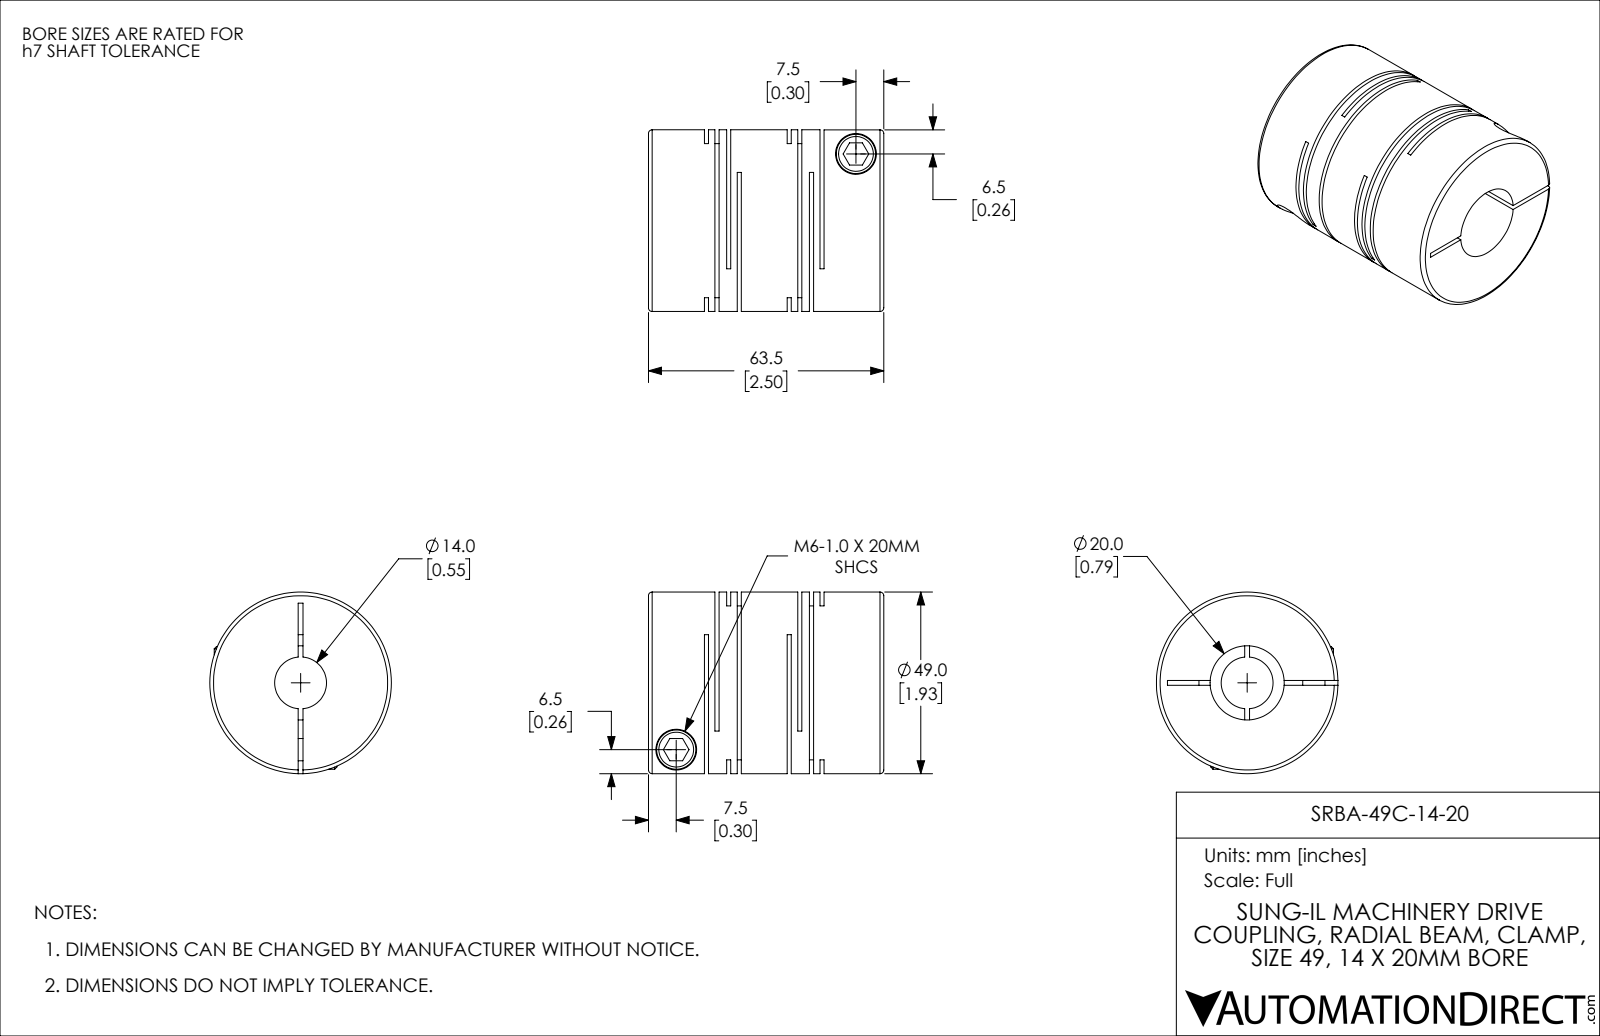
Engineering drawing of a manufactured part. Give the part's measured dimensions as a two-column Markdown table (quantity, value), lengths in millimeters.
| quantity | value |
| --- | --- |
| part name | SRBA-49C-14-20 |
| STEP written by | SolidWorks 2021 (CONFIG_CONTROL_DESIGN) |
| units | millimeters |
| bodies | 1 solid, 114 faces (60 planar, 42 cylindrical, 12 other) |
| overall size | 63.5 × 49 × 49 |
| volume | 88 531 mm³ |
| surface area | 38 170 mm² |
| round holes (diameter × count) | 6 × 2, 11 × 2, 14 × 1, 20 × 1 |
| round bosses / shafts (diameter × count) | 10.6 × 2, 49 × 1 |
| main face-to-face distances | 6, 1.1, 2.85, 22.35, 1.75, 4.9, 21.25, 3.15, 19.5, 16.35 |
